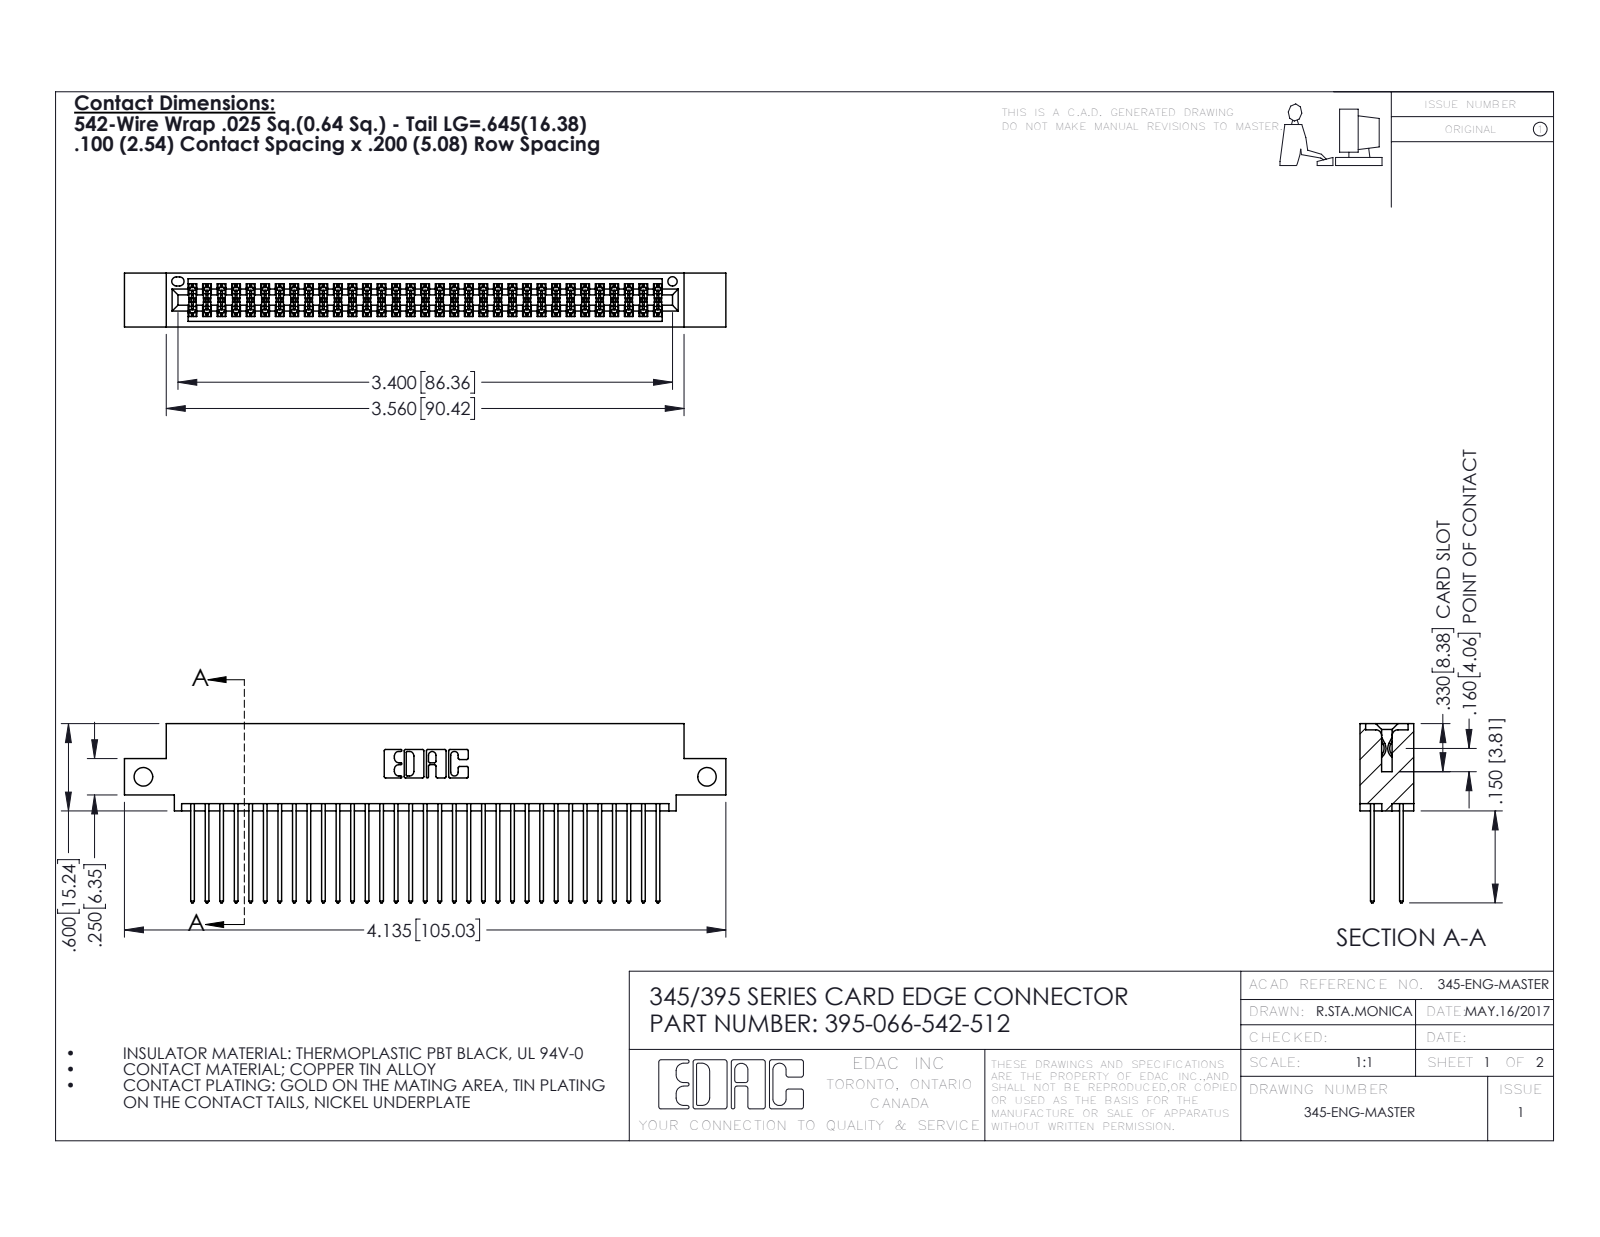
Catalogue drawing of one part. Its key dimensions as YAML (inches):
part_name: "345-292-001_345-293-142; 395-066-542-512; 345 Part_0.110 Offset - Side Mount"
step_written_by: "SolidWorks 2016 (CONFIG_CONTROL_DESIGN)"
units: inches
bodies: {solids: 67, faces: 3430, planar: 2262, cylindrical: 1168, other: 0}
overall_size: [4.135, 1.232, 0.37]
volume: 0.626
surface_area: 25.41
round_holes:
  - {diameter: 0.128, count: 2}
  - {diameter: 0.064, count: 1}
partial_cylinders:
  - {radius: 0.006, count: 99}
  - {radius: 0.01, count: 66}
  - {radius: 0.01, count: 22}
  - {radius: 0.007, count: 6}
  - {radius: 0.031, count: 6}
  - {radius: 0.026, count: 3}
  - {radius: 0.014, count: 2}
  - {radius: 0.019, count: 2}
face_to_face_distances: [0.298, 0.072, 0.2, 0.098, 0.272, 0.025, 0.37, 0.225, 0.175, 0.149]
hole_center_spacings: [3.875]
